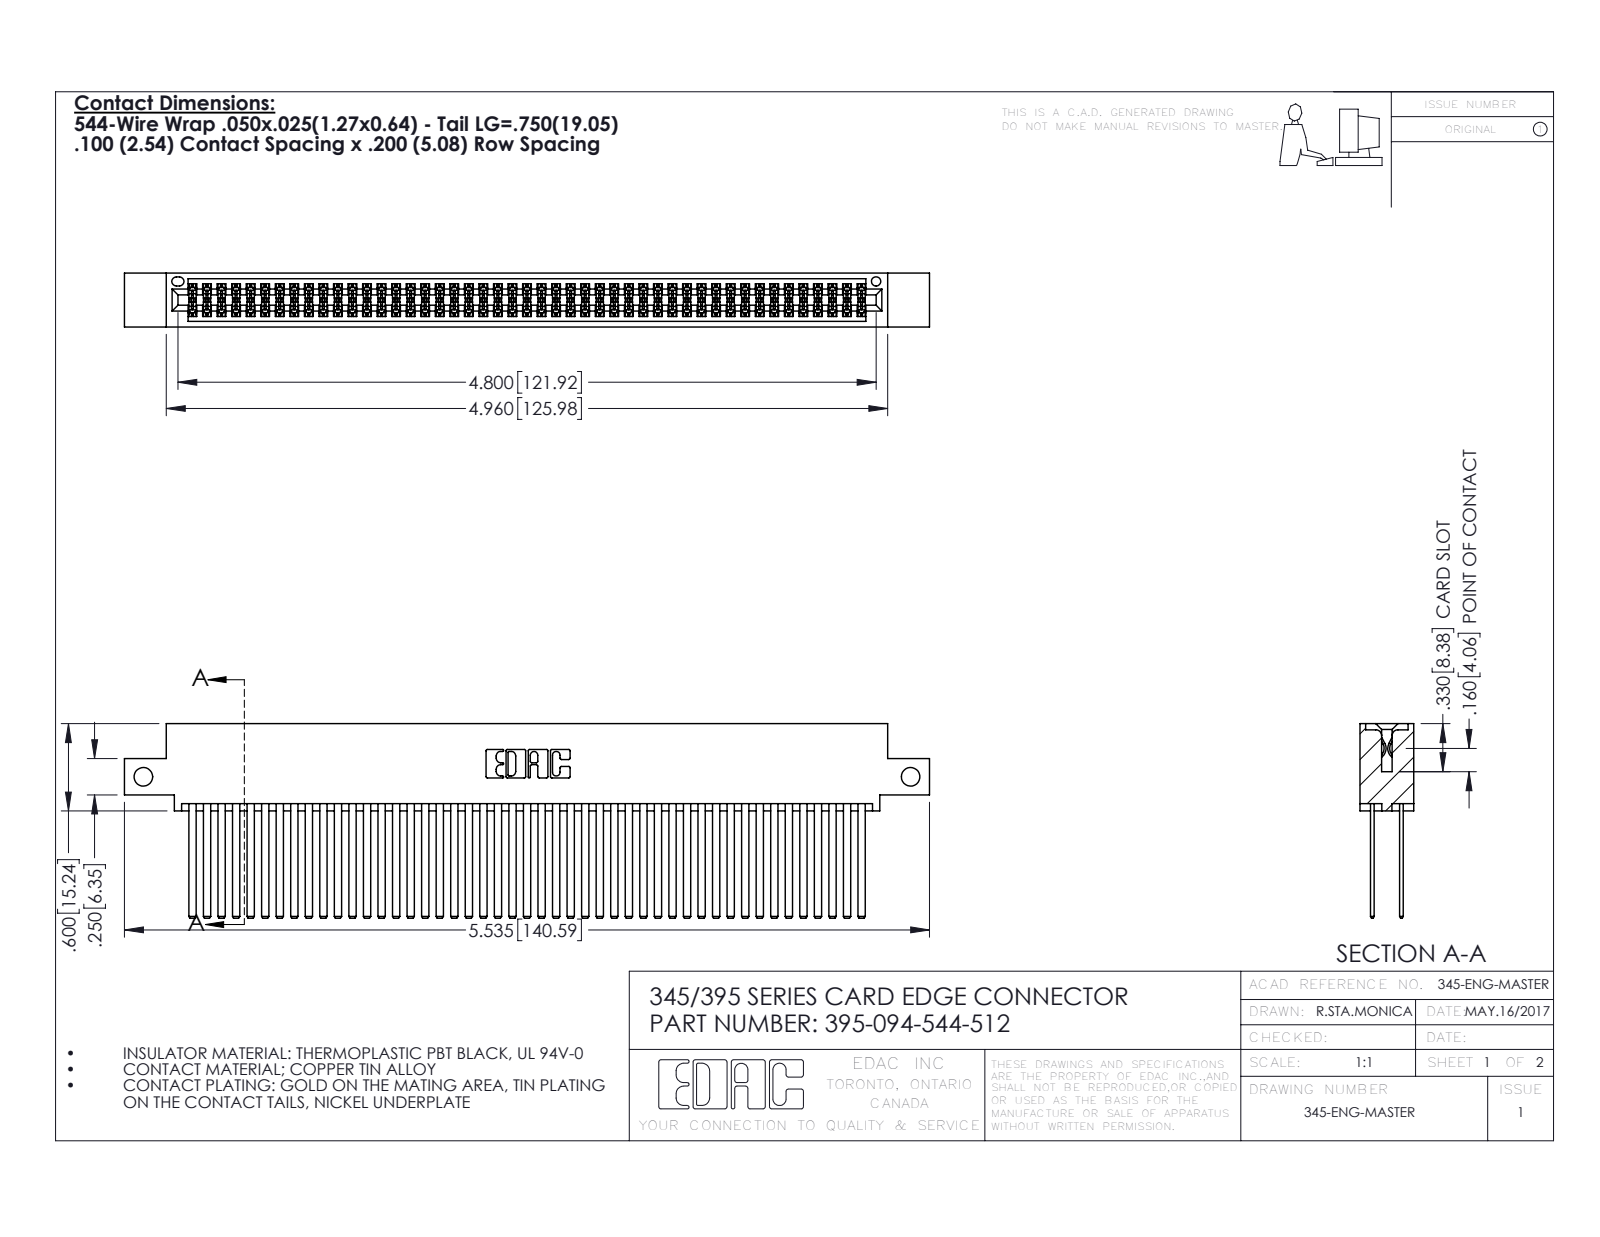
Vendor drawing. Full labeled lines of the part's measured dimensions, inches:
Part name (STEP PRODUCT): 395-094-544-512; 345-292-001_345-293-144; 345 Part_0.110 Offset - Side Mount
STEP written by: SolidWorks 2016 (CONFIG_CONTROL_DESIGN)
Units: inches
Bodies: 95 solids, 4266 faces (2810 planar, 1456 cylindrical, 0 other)
Overall size (bounding box): 5.535 × 1.337 × 0.37
Volume: 0.907 in³ · Surface area: 40.12 in²
Round holes (diameter × count): ⌀0.128 ×2, ⌀0.064 ×1
Partial cylindrical surfaces — rounded edges, fillets, slot ends (radius × count): R0.006 ×141, R0.01 ×22, R0.007 ×6, R0.031 ×6, R0.026 ×3, R0.014 ×2, R0.019 ×2, R0.022 ×2
Main face-to-face distances: 0.2, 0.025, 0.298, 0.072, 0.098, 0.272, 0.225, 0.175, 0.37, 0.05
Hole centre spacings: 5.275
